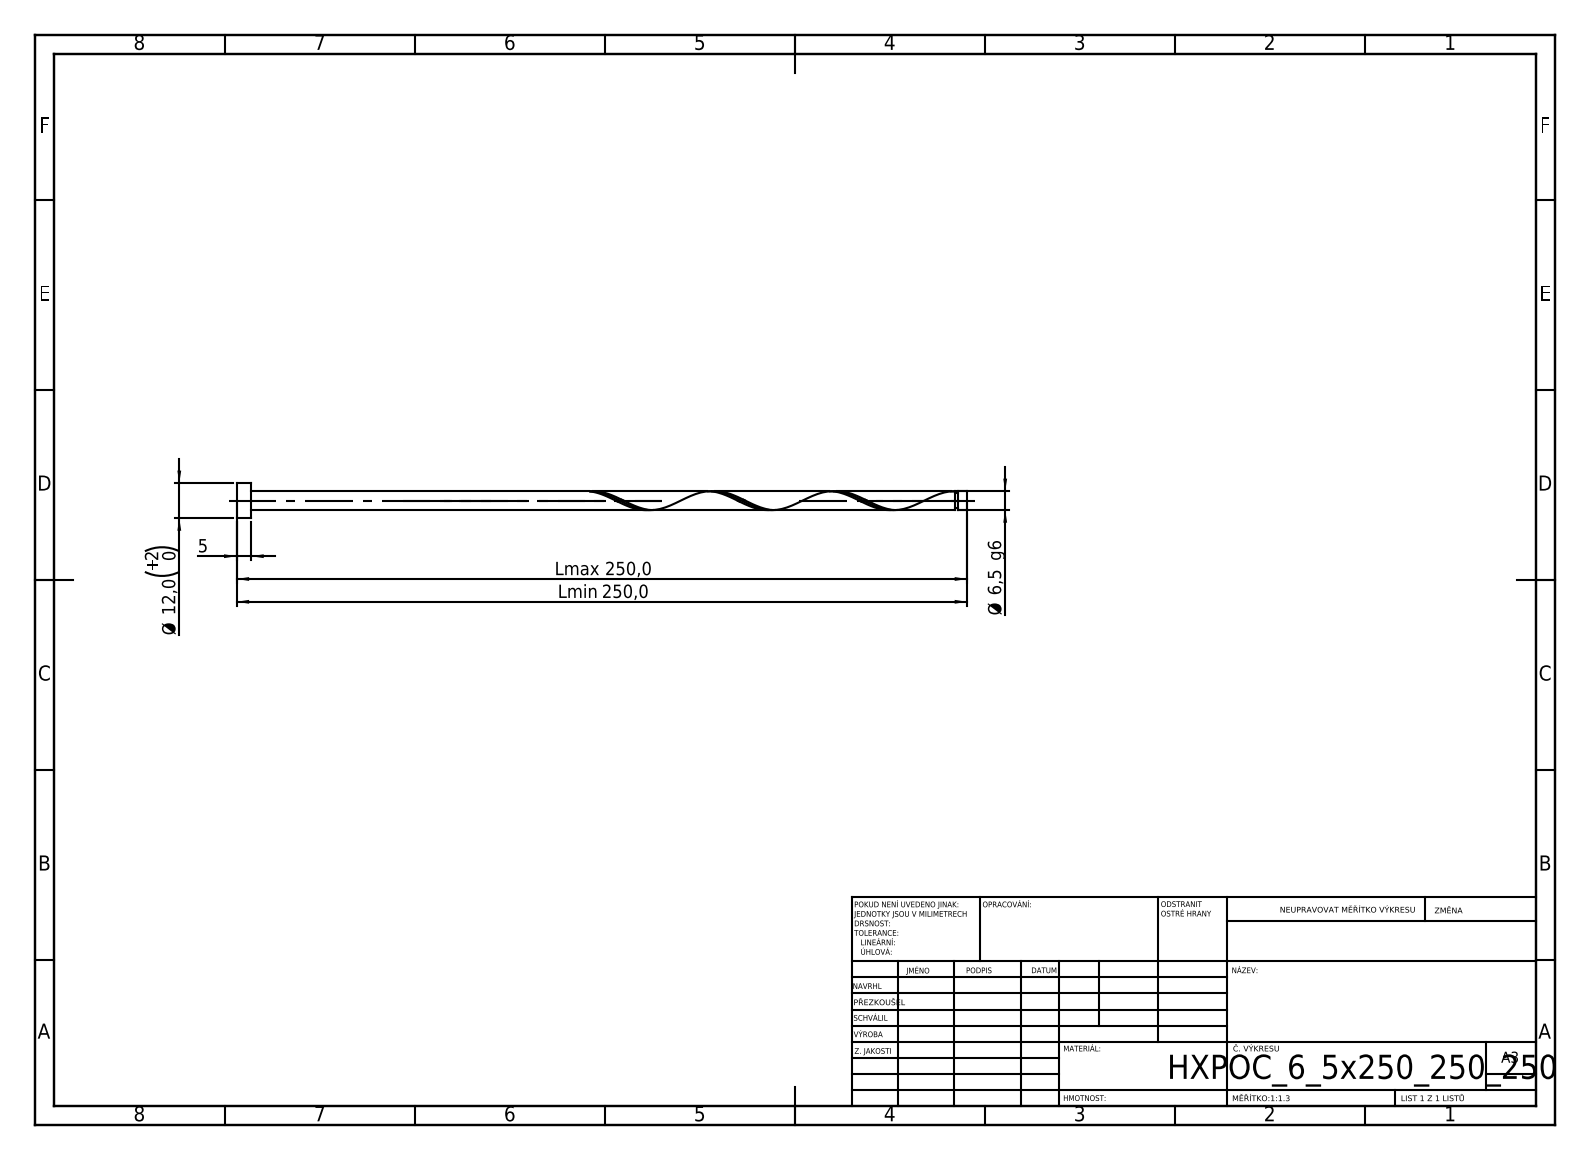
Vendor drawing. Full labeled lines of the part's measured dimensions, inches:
STEP written by: SolidWorks 2019 (CONFIG_CONTROL_DESIGN)
Units: inches
Bodies: 1 solid, 21 faces (6 planar, 14 cylindrical, 1 other)
Overall size (bounding box): 9.843 × 0.472 × 0.472
Volume: 0.525 in³ · Surface area: 8.564 in²
Round bosses / shafts (diameter × count): ⌀0.472 ×1, ⌀0.256 ×1, ⌀0.205 ×1
Main face-to-face distances: 0.197, 9.843, 9.646, 9.724, 9.527, 0.119, 9.673, 9.476, 0.051, 0.17
